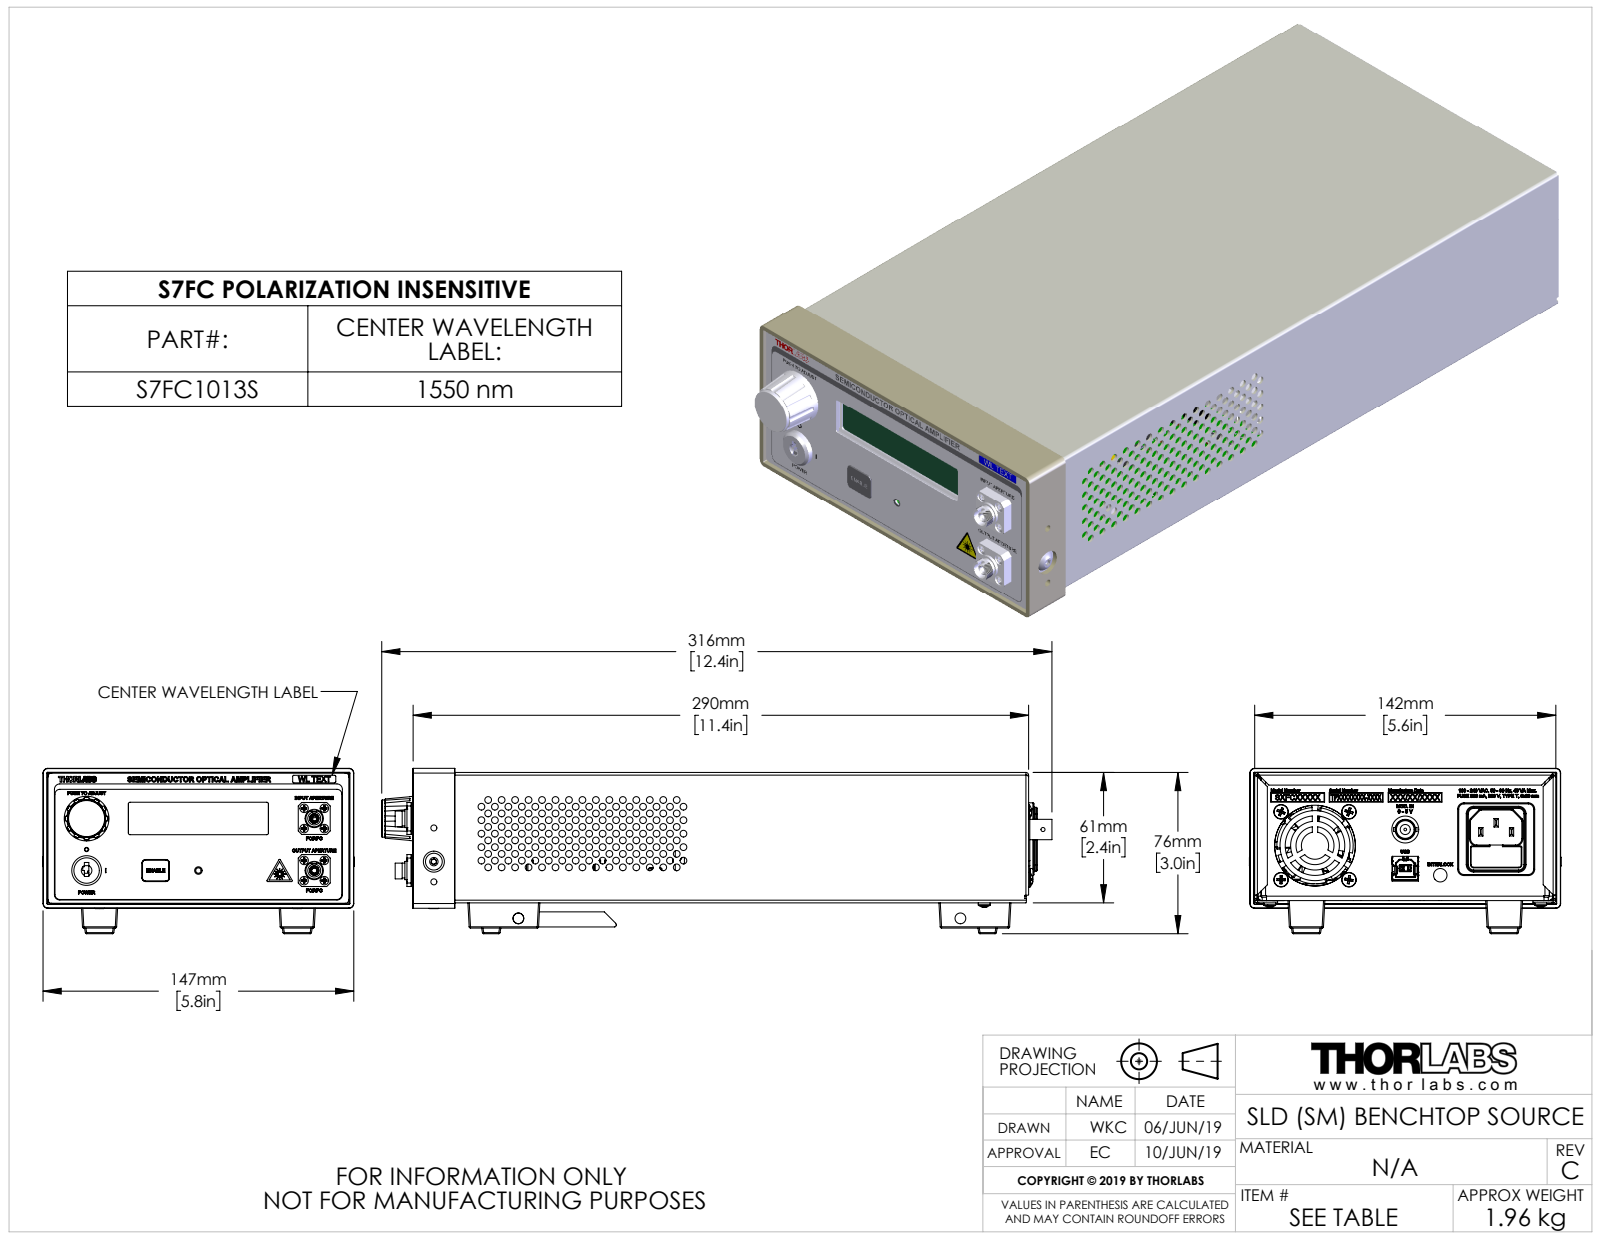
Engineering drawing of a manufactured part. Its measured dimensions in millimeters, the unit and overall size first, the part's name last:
Units: millimetres
Overall size (bounding box): 316 × 147 × 78
Round holes (diameter × count): ⌀3.2 ×170, ⌀0.9 ×44, ⌀1 ×16, ⌀1 ×16, ⌀0.8 ×14, ⌀4 ×12, ⌀1.8 ×8, ⌀2.2 ×8, ⌀2.6 ×8, ⌀3 ×8, ⌀3.1 ×8, ⌀3.6 ×7
Round bosses / shafts (diameter × count): ⌀3.8 ×9, ⌀4.2 ×8, ⌀4.2 ×8, ⌀3 ×8, ⌀2.2 ×8, ⌀3.5 ×6, ⌀0.5 ×6, ⌀6.9 ×5
Partial cylindrical surfaces — rounded edges, fillets, slot ends (radius × count): R0.5 ×51, R0.6 ×48, R0.1 ×32, R0.3 ×20, R1.3 ×17, R0.3 ×15, R3 ×14, R0.5 ×9
Main face-to-face distances: 1, 1.6, 60.4, 6.4, 59.4, 57.8, 58.8, 7.9, 51.5, 52.5
Hole centre spacings: 12.7, 31.8, 6.4, 25.4, 19.1, 26.2, 28.4, 38.1
Bodies: 0 solids, 13292 faces (7670 planar, 1237 cylindrical, 4385 other)
Part name (STEP PRODUCT): TTN012401-E0W
STEP written by: SolidWorks 2018 (CONFIG_CONTROL_DESIGN)
